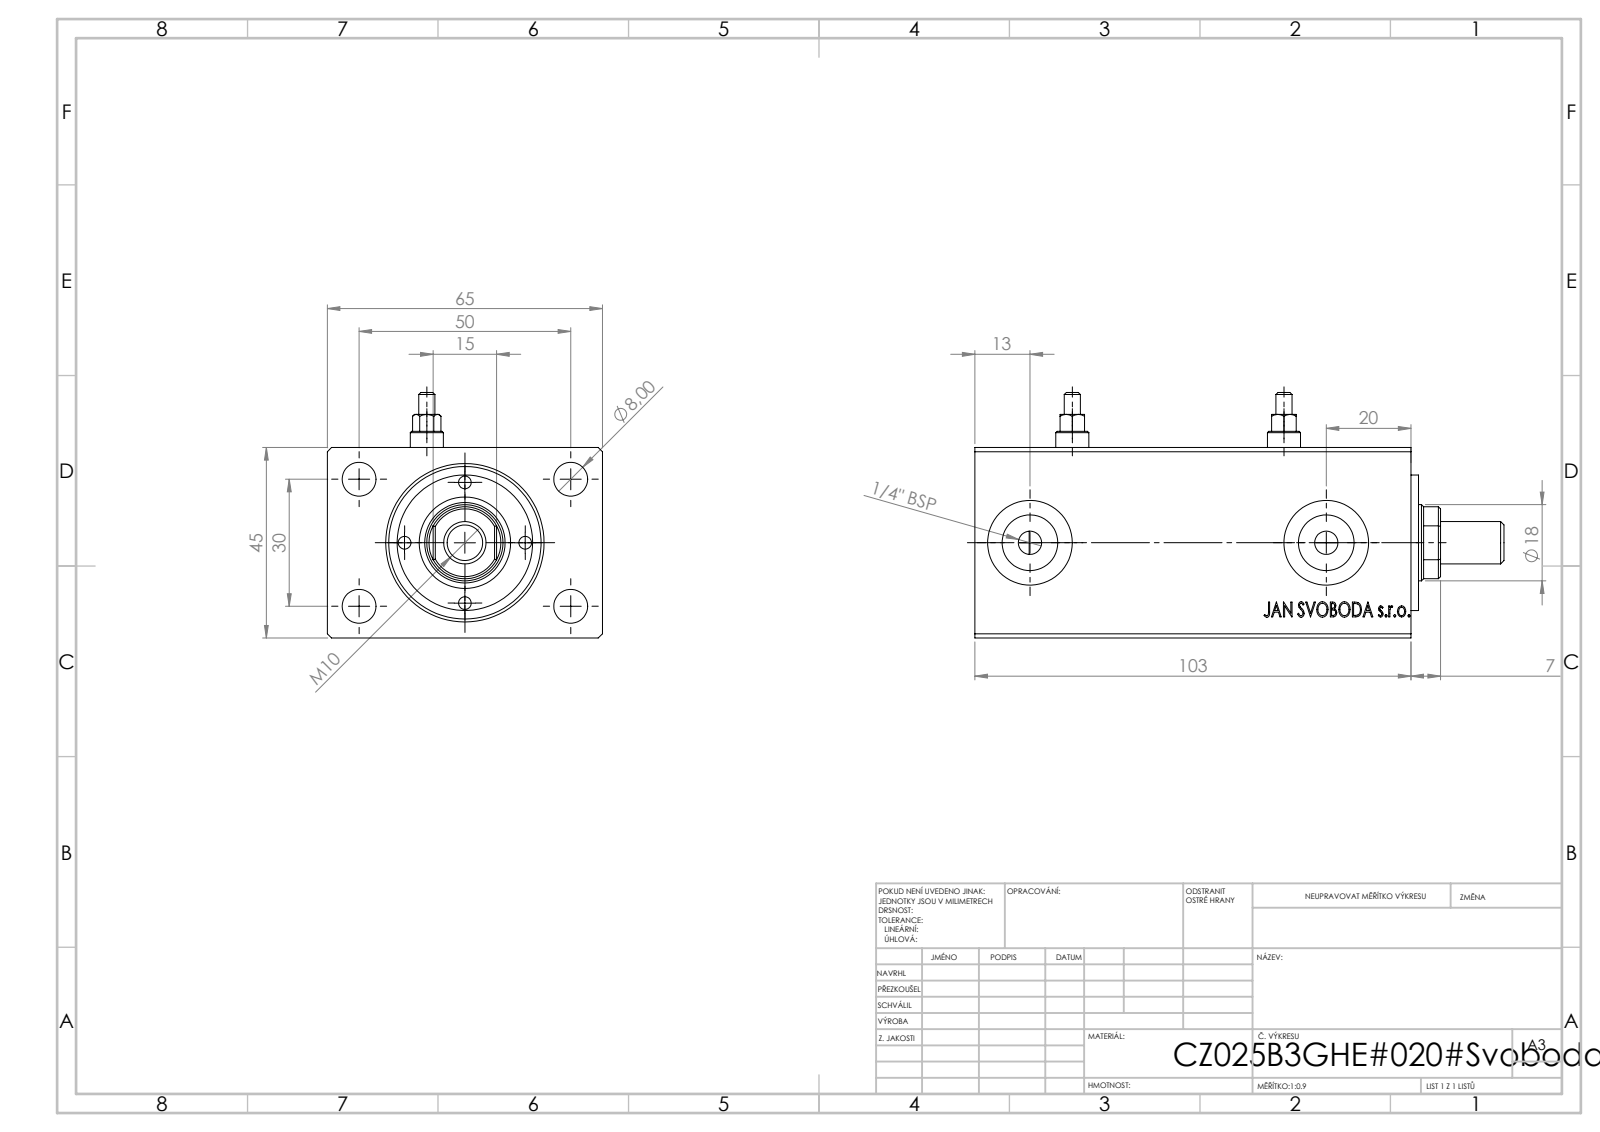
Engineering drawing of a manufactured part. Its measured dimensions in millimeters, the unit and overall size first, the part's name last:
Units: millimetres
Overall size (bounding box): 125 × 65 × 58
Round holes (diameter × count): ⌀8 ×6, ⌀3 ×4, ⌀1.8 ×2, ⌀5.5 ×2, ⌀13.16 ×2, ⌀20 ×2, ⌀8.5 ×1, ⌀18 ×1, ⌀19 ×1, ⌀25 ×1, ⌀36 ×1
Round bosses / shafts (diameter × count): ⌀7.8 ×2, ⌀3.8 ×2, ⌀32 ×1, ⌀10 ×1
Partial cylindrical surfaces — rounded edges, fillets, slot ends (radius × count): R8.5 ×1
Main face-to-face distances: 45, 65, 103, 7, 102.8, 5.2, 12.8, 90.2, 12.6, 1.8
Hole centre spacings: 14.25, 18.45, 20.15, 25.01, 29.15, 38.48, 42.02, 50
Volume: 283 912 mm³ · Surface area: 54 288 mm²
Bodies: 6 solids, 939 faces (425 planar, 76 cylindrical, 438 other)
Part name (STEP PRODUCT): Zatka_Cushioning3; V500CZ; V500CZ_B_VC; V500CZ_SMALL_MALE_METRIC
STEP written by: SolidWorks 2019 (CONFIG_CONTROL_DESIGN)
